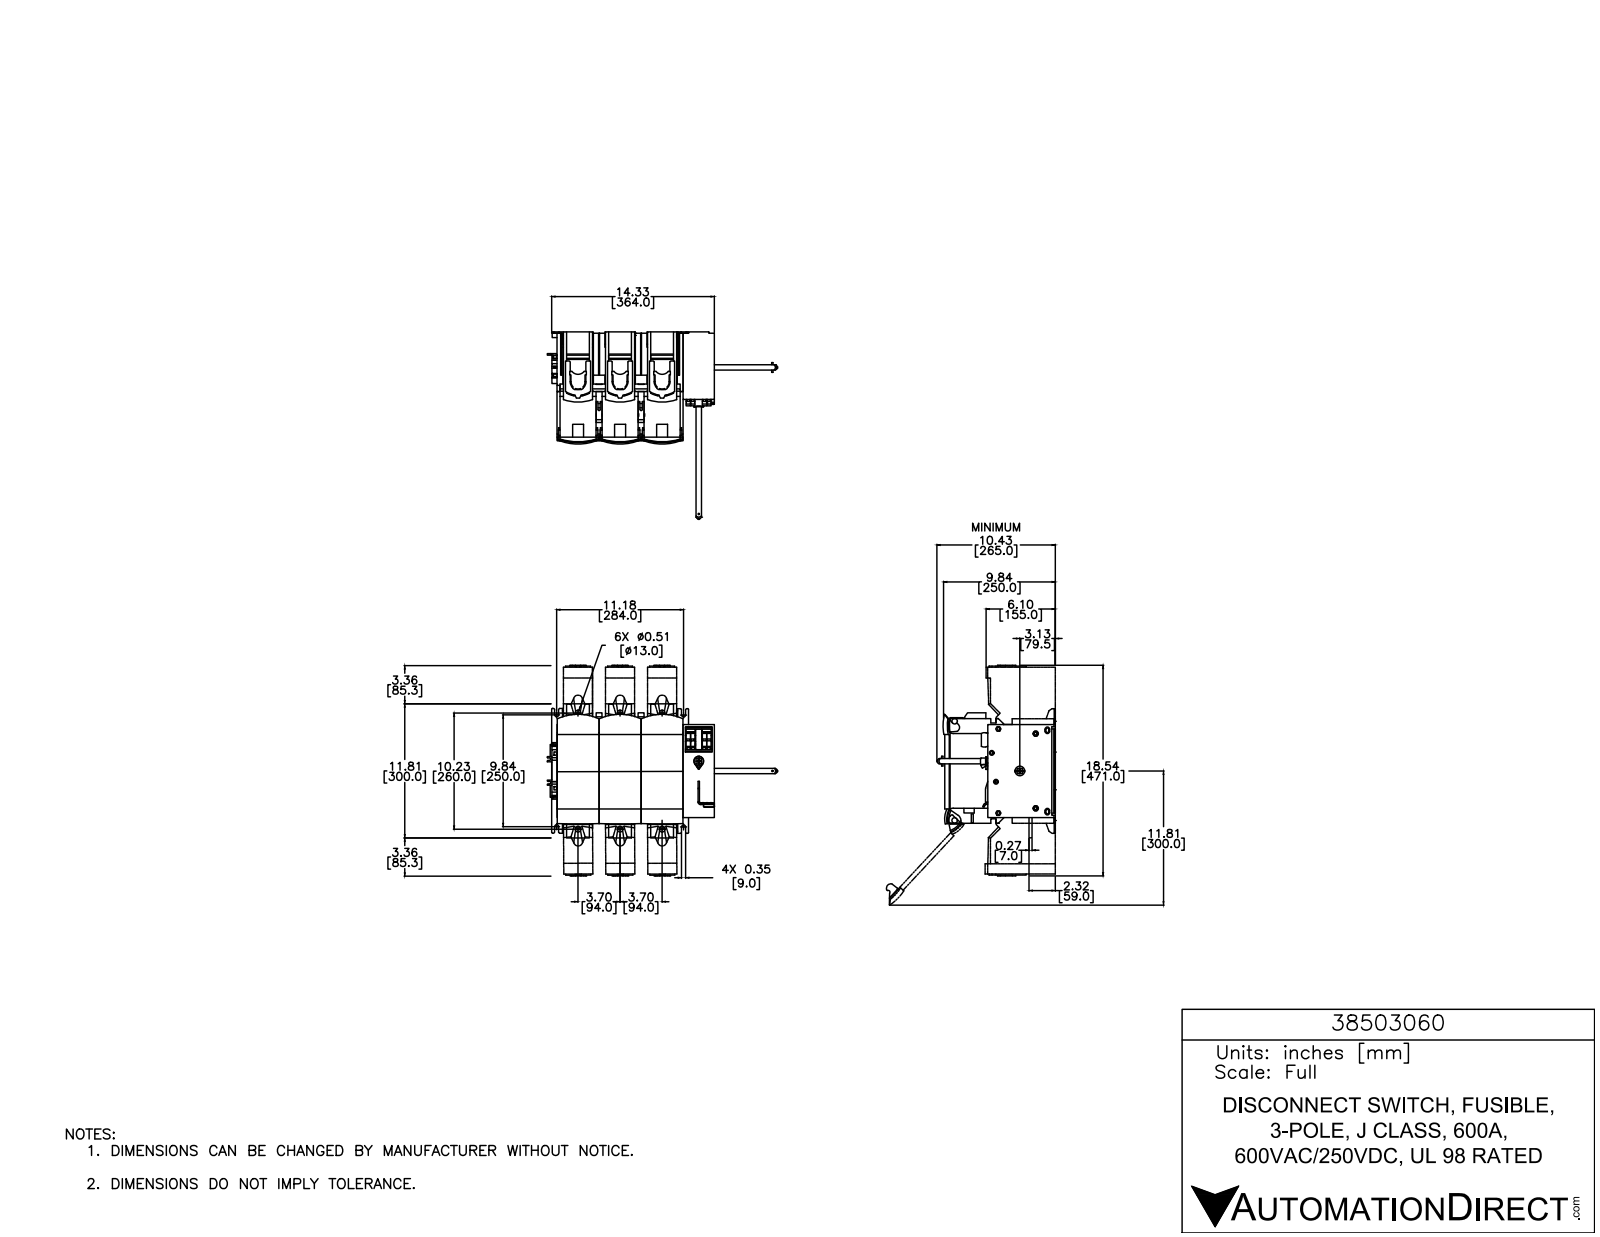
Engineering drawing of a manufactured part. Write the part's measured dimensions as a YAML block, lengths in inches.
part_name: "38503060"
step_written_by: "SolidWorks 2015 (AUTOMOTIVE_DESIGN)"
units: inches
bodies: {solids: 23, faces: 2454, planar: 2012, cylindrical: 379, other: 63}
overall_size: [15.169, 14.331, 9.883]
volume: 995.6
surface_area: 2487
round_holes:
  - {diameter: 0.256, count: 6}
  - {diameter: 0.512, count: 6}
  - {diameter: 0.11, count: 4}
  - {diameter: 0.118, count: 4}
  - {diameter: 0.165, count: 4}
  - {diameter: 0.413, count: 4}
  - {diameter: 0.295, count: 3}
  - {diameter: 0.315, count: 3}
  - {diameter: 0.461, count: 2}
  - {diameter: 0.63, count: 2}
  - {diameter: 0.209, count: 1}
  - {diameter: 0.472, count: 1}
round_bosses_or_shafts:
  - {diameter: 0.445, count: 2}
  - {diameter: 0.866, count: 1}
  - {diameter: 0.472, count: 1}
  - {diameter: 0.295, count: 1}
partial_cylinders:
  - {radius: 0.01, count: 16}
  - {radius: 0.039, count: 11}
  - {radius: 0.014, count: 8}
  - {radius: 0.047, count: 8}
  - {radius: 0.079, count: 7}
  - {radius: 0.098, count: 6}
  - {radius: 0.689, count: 6}
  - {radius: 1.516, count: 6}
face_to_face_distances: [3.701, 0.512, 0.098, 7.402, 2.461, 10.591, 2.622, 2.559, 0.063, 3.693]
hole_center_spacings: [0.827, 1.541, 2.666, 3.572, 3.701, 5.112, 10.885, 6.575]
